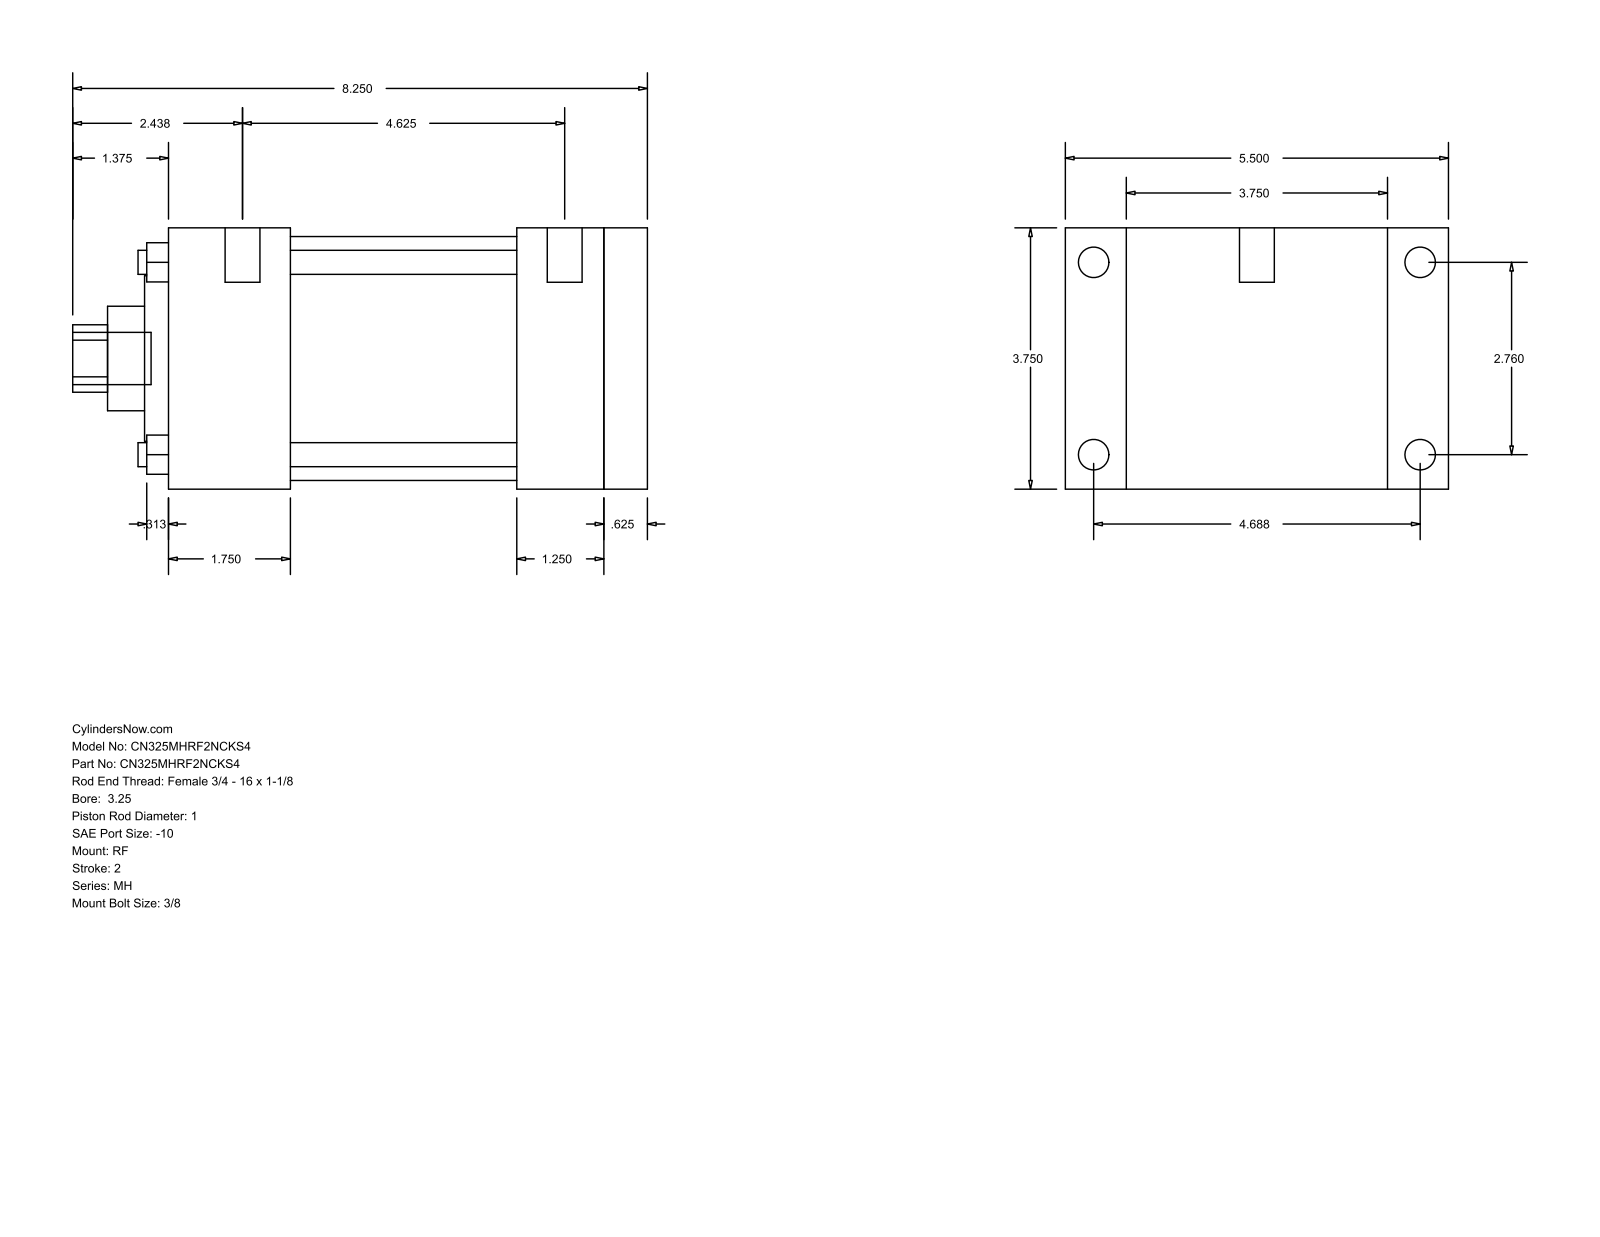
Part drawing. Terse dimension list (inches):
name: MH_RF__0325_1
written by: GSSL Pune (CONFIG_CONTROL_DESIGN)
unit: in
bodies: 0 solids, 94 faces (65 planar, 29 cylindrical, 0 other)
size: 8.25 × 5.5 × 3.75
holes: 4× ⌀0.345, 1× ⌀1, 1× ⌀1.5, 1× ⌀2.375, 1× ⌀3.5
bosses: 4× ⌀0.438, 4× ⌀0.219, 2× ⌀0.5, 1× ⌀0.75
rounds: 1× R0.484
face distances: 3.75, 6.875, 0.625, 6.25, 0.875, 4.625, 1.75, 4.5, 5.125, 5
hole spacings: 1.952, 2.76, 3.903
